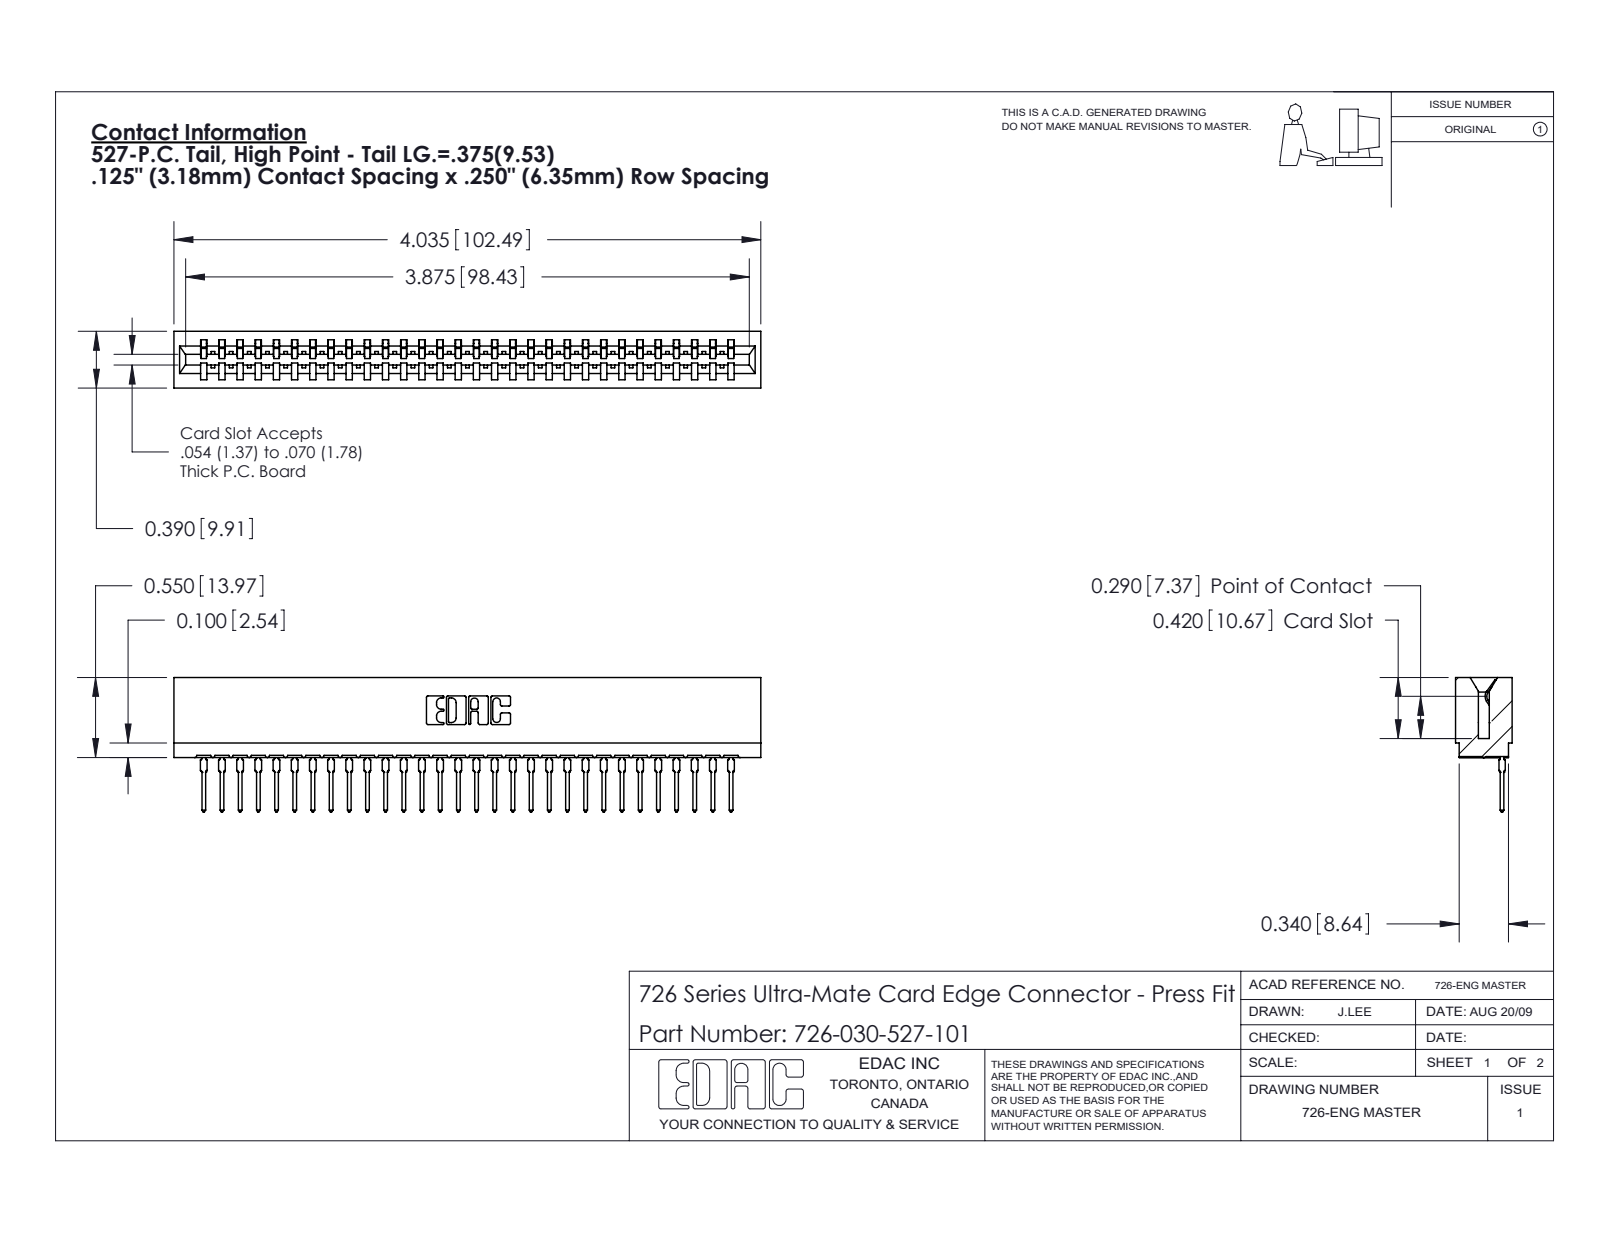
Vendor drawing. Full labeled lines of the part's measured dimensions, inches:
Part name (STEP PRODUCT): 746-292-001_527; 726-030-527-101; 726 Part_.515 Slot Depth - 01
STEP written by: SolidWorks 2020 (CONFIG_CONTROL_DESIGN)
Units: inches
Bodies: 31 solids, 3337 faces (1945 planar, 612 cylindrical, 780 other)
Overall size (bounding box): 4.035 × 0.924 × 0.39
Volume: 0.564 in³ · Surface area: 21.87 in²
Partial cylindrical surfaces — rounded edges, fillets, slot ends (radius × count): R0.021 ×60, R0.015 ×31, R0.01 ×22, R0.007 ×6, R0.031 ×6, R0.005 ×4, R0.011 ×4, R0.026 ×3
Main face-to-face distances: 0.057, 0.333, 0.39, 0.25, 0.025, 0.307, 0.5, 0.083, 0.75, 0.275
